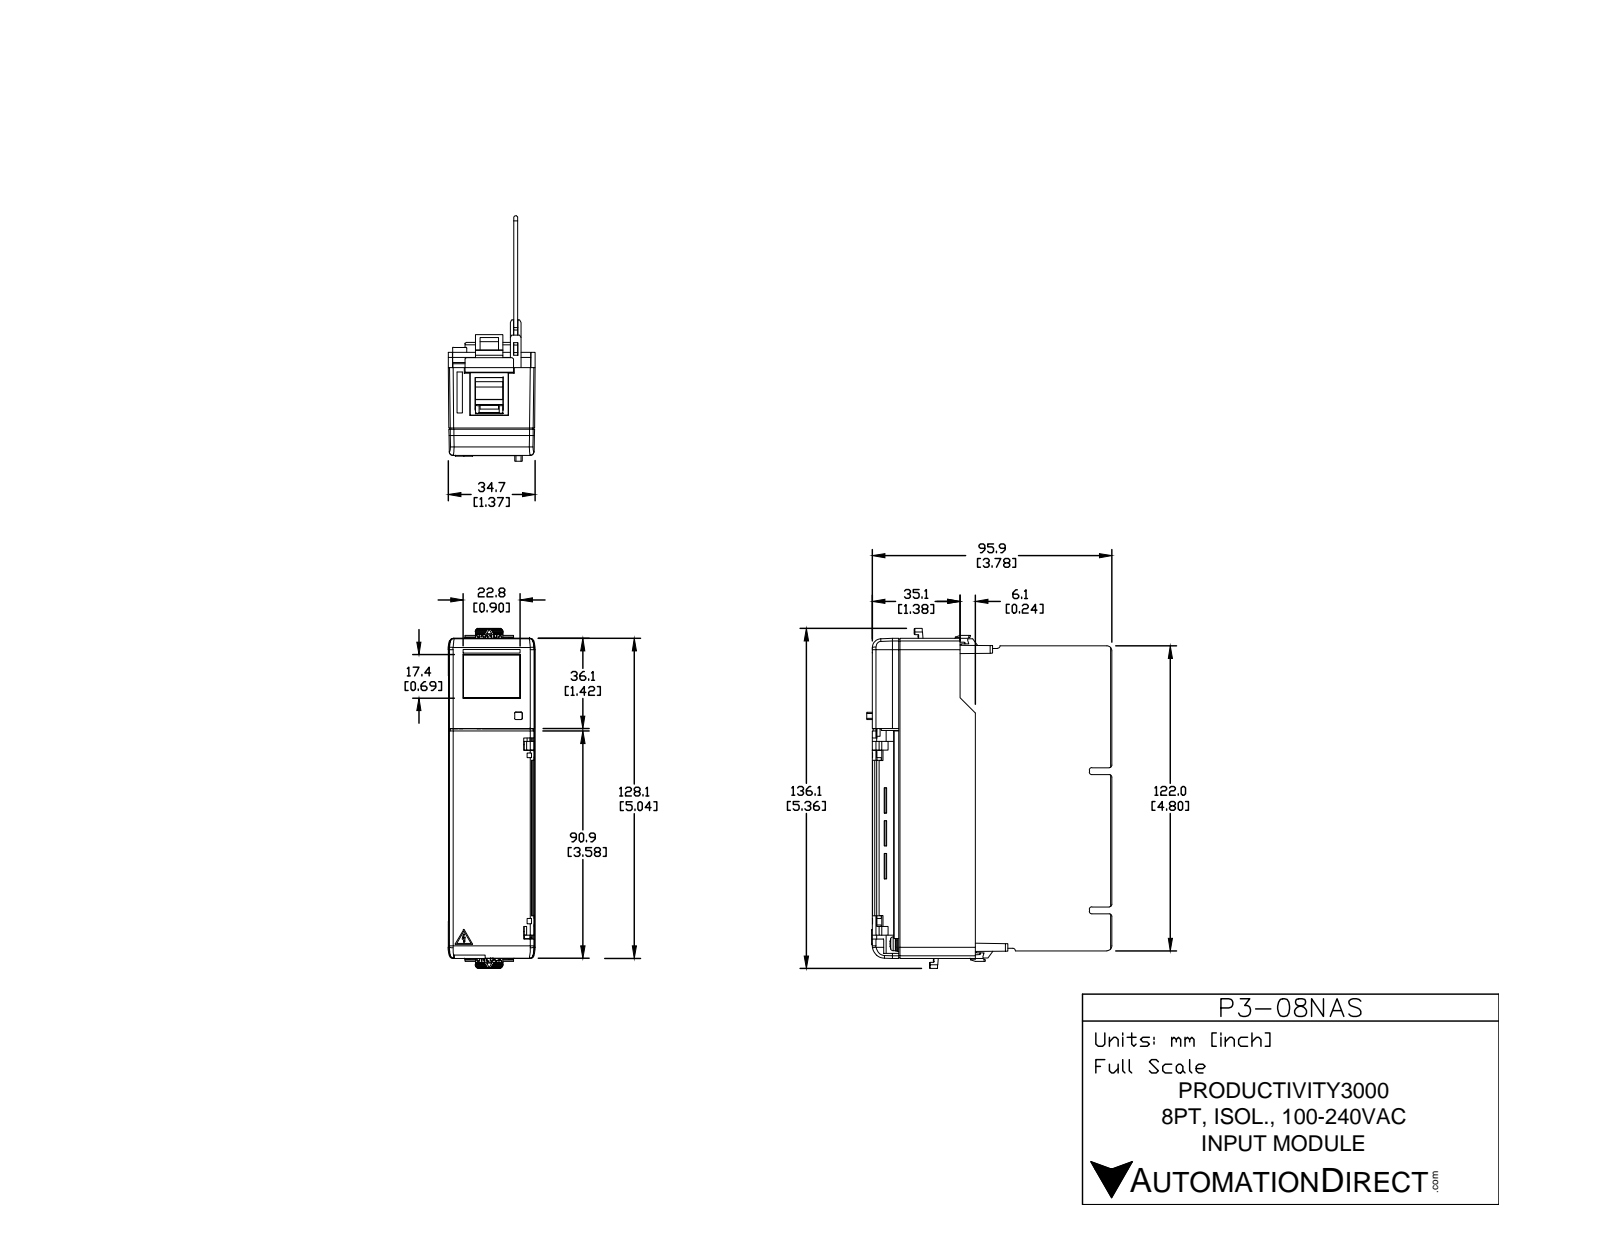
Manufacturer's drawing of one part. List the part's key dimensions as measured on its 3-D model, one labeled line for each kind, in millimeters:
Part name (STEP PRODUCT): P3-08NAS
STEP written by: SolidWorks 2009 (CONFIG_CONTROL_DESIGN)
Units: millimetres
Bodies: 1 solid, 3804 faces (2821 planar, 737 cylindrical, 246 other)
Overall size (bounding box): 136.08 × 96.19 × 34.8
Volume: 101 334 mm³ · Surface area: 75 406 mm²
Round holes (diameter × count): ⌀3.2 ×22, ⌀5 ×2, ⌀1.8 ×1
Round bosses / shafts (diameter × count): ⌀5.5 ×22, ⌀3 ×22, ⌀2.4 ×20, ⌀5.6 ×2, ⌀2.2 ×2, ⌀2 ×2, ⌀1.5 ×1
Partial cylindrical surfaces — rounded edges, fillets, slot ends (radius × count): R0.5 ×91, R1 ×33, R0.3 ×29, R1.67 ×22, R1.5 ×13, R2 ×6, R0.2 ×5, R0.1 ×4
Main face-to-face distances: 1.6, 1.7, 28.23, 26.53, 32.56, 22.2, 2.2, 7.9, 6.8, 5.32
Hole centre spacings: 8.68, 7.62, 13.84, 15.24, 20.59, 22.86, 27.79, 30.48
